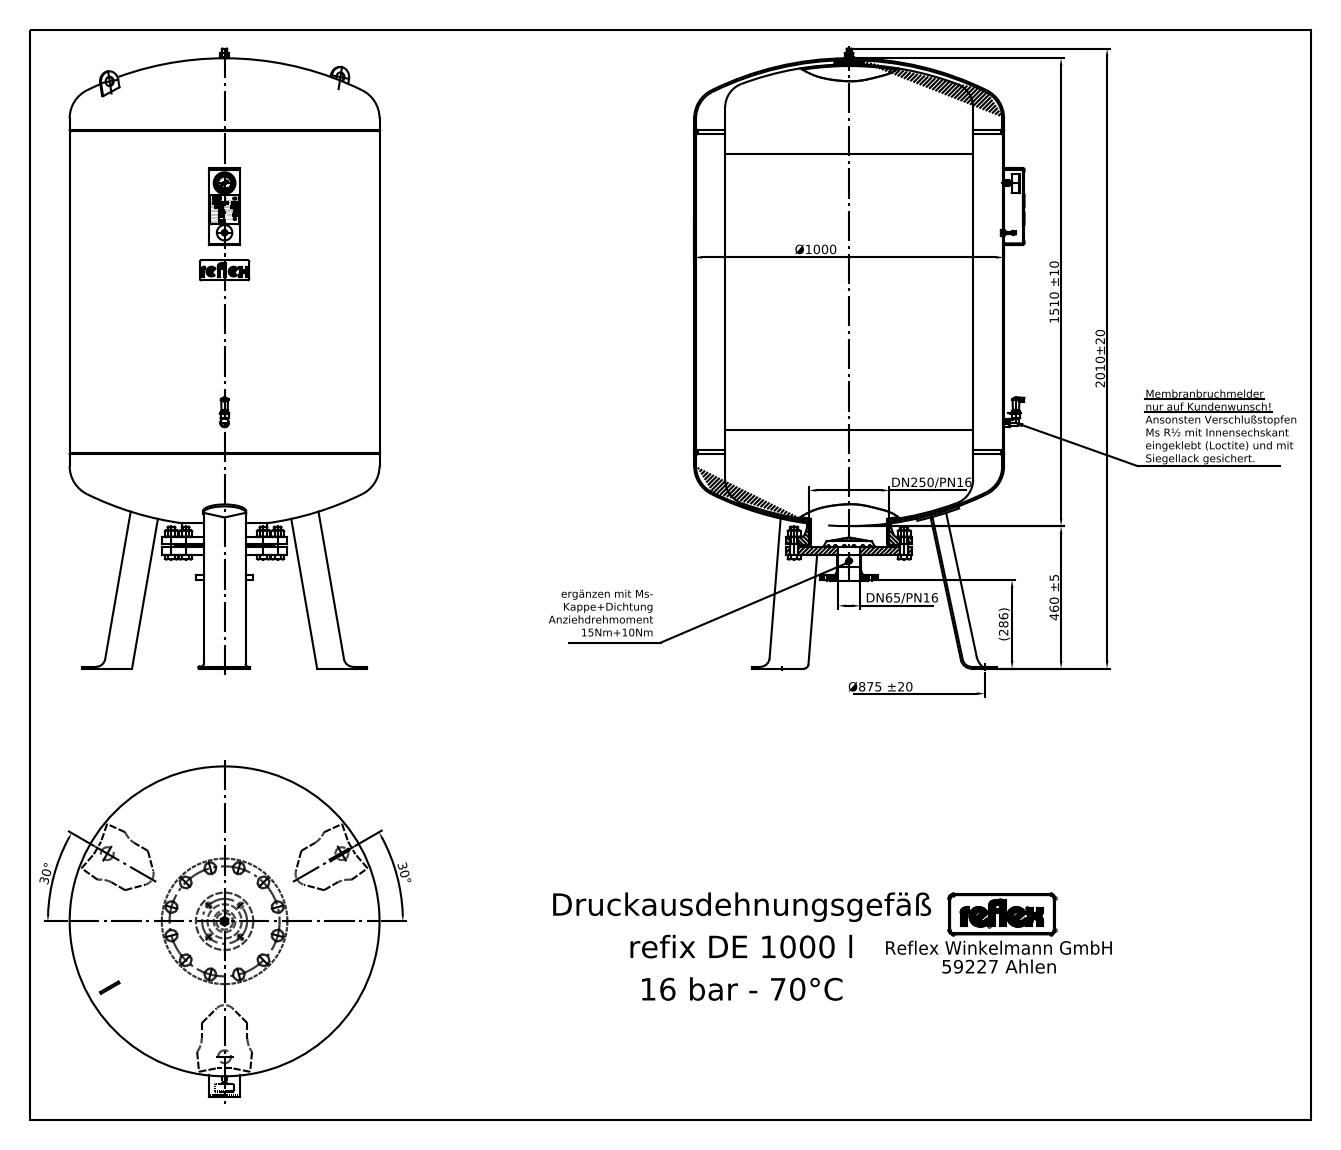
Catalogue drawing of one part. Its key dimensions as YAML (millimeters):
step_written_by: "Mechanical Desktop 2008 (CONFIG_CONTROL_DESIGN)"
units: millimeters
bodies: {solids: 23, faces: 612, planar: 340, cylindrical: 155, other: 117}
overall_size: [2010, 1066, 1000]
volume: 1090000000
surface_area: 10330000
round_holes:
  - {diameter: 10, count: 1}
  - {diameter: 30, count: 1}
  - {diameter: 50, count: 1}
  - {diameter: 69, count: 1}
  - {diameter: 260.4, count: 1}
round_bosses_or_shafts:
  - {diameter: 16, count: 13}
  - {diameter: 28, count: 2}
  - {diameter: 26, count: 2}
  - {diameter: 20, count: 2}
  - {diameter: 1000, count: 1}
  - {diameter: 405, count: 1}
  - {diameter: 273, count: 1}
  - {diameter: 76.1, count: 1}
partial_cylinders:
  - {radius: 25, count: 18}
  - {radius: 5.62, count: 4}
  - {radius: 2.25, count: 3}
  - {radius: 9, count: 3}
  - {radius: 1, count: 2}
  - {radius: 3.84, count: 2}
  - {radius: 5, count: 2}
  - {radius: 6.75, count: 2}
face_to_face_distances: [1075, 26, 274.5, 1349.5, 300.5, 1375.5, 31, 57, 243.5, 1318.5]
hole_center_spacings: [82.33, 515.5]
